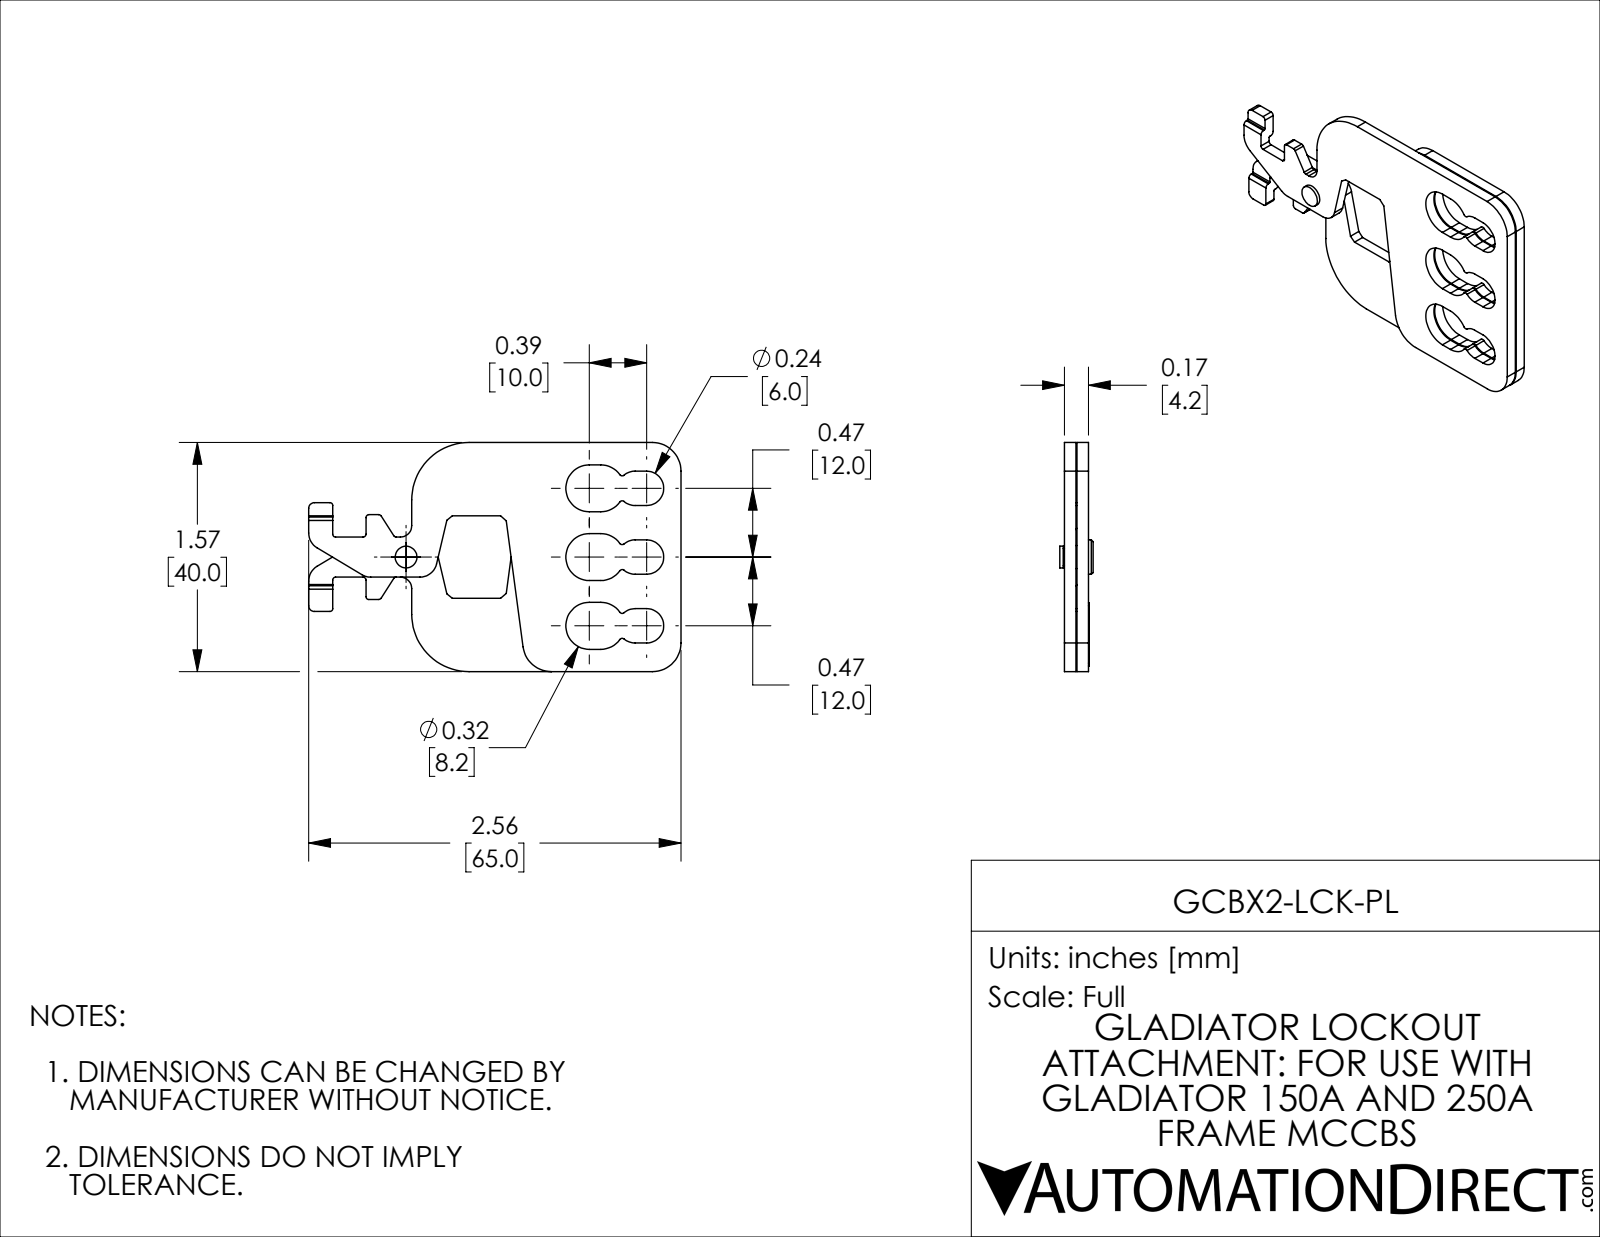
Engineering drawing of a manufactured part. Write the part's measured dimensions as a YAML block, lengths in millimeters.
part_name: "GCBX2-LCK-PL"
step_written_by: "SolidWorks 2021 (CONFIG_CONTROL_DESIGN)"
units: millimeters
bodies: {solids: 1, faces: 939, planar: 829, cylindrical: 108, other: 2}
overall_size: [65, 40, 5.8]
volume: 4930
surface_area: 6426
round_holes:
  - {diameter: 3.1, count: 1}
  - {diameter: 4.2, count: 1}
round_bosses_or_shafts:
  - {diameter: 6, count: 1}
  - {diameter: 4, count: 1}
  - {diameter: 3.8, count: 1}
  - {diameter: 3, count: 1}
partial_cylinders:
  - {radius: 0.5, count: 22}
  - {radius: 3, count: 12}
  - {radius: 4.1, count: 6}
  - {radius: 0.2, count: 4}
  - {radius: 0.6, count: 4}
  - {radius: 5, count: 4}
  - {radius: 1, count: 2}
  - {radius: 2, count: 2}
face_to_face_distances: [2, 2.2, 4.2, 2.3, 2.1, 4.3, 40, 1, 3, 0.8]
